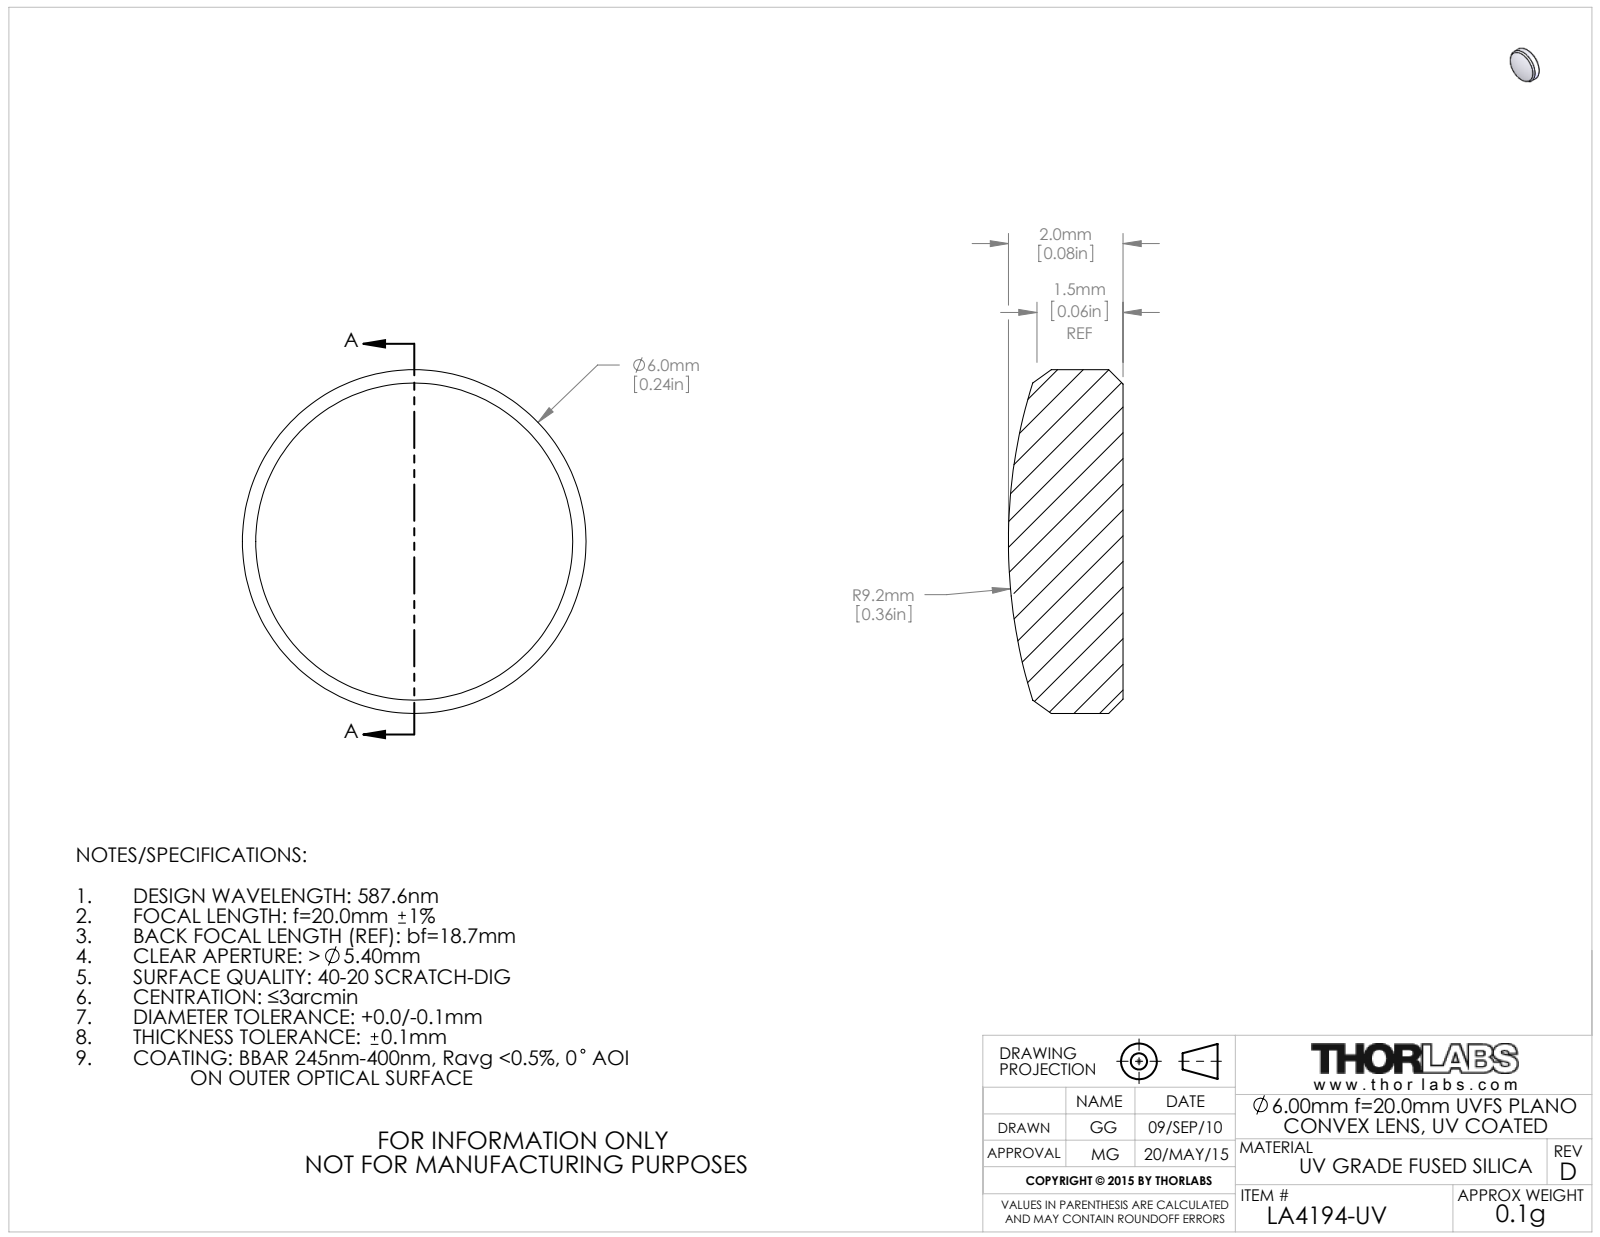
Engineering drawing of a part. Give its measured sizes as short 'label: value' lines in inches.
name: 4270-E0W
written by: SolidWorks 2014 (CONFIG_CONTROL_DESIGN)
unit: in
bodies: 1 solid, 9 faces (1 planar, 2 cylindrical, 6 other)
size: 0.236 × 0.236 × 0.079
volume: 0.003 in³; area: 0.13 in²
bosses: 1× ⌀0.236
